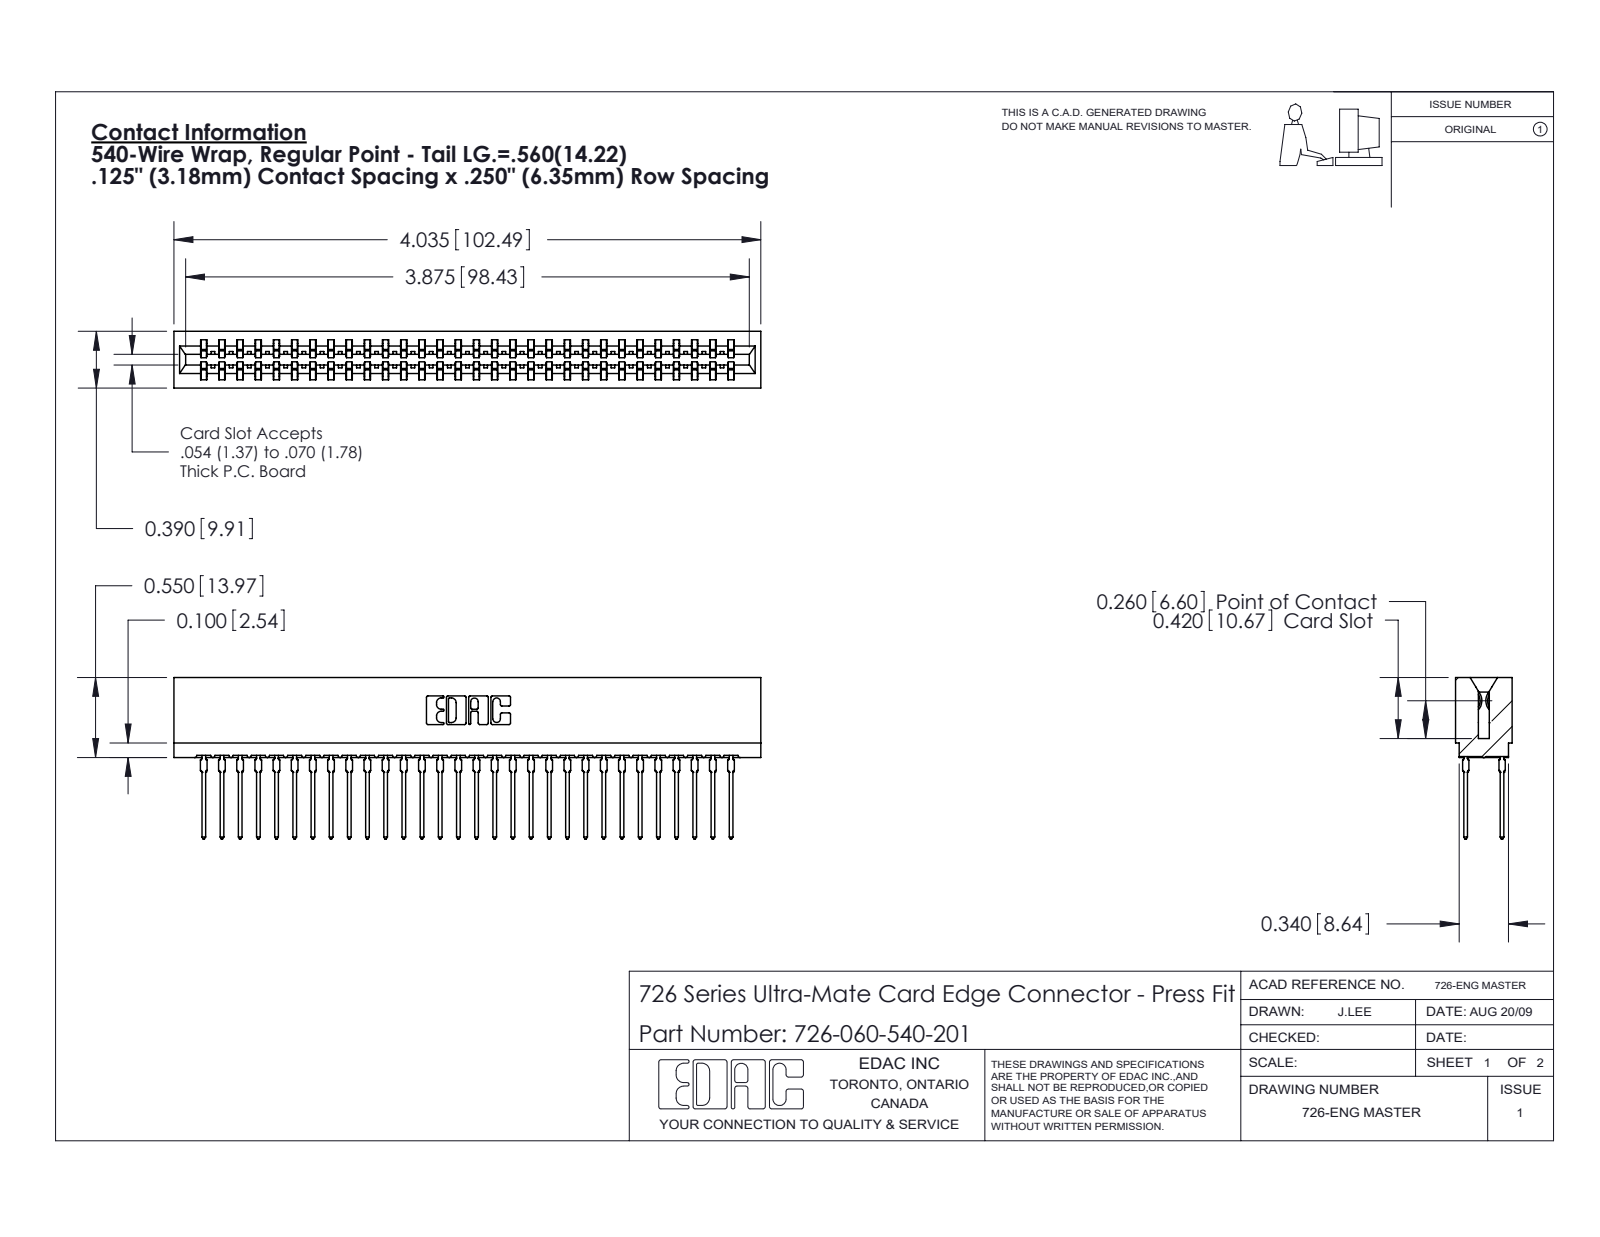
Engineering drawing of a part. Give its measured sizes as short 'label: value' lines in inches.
name: 726 Part_.515 Slot Depth - 01; 746-292-001_540; 726-060-540-201
written by: SolidWorks 2020 (CONFIG_CONTROL_DESIGN)
unit: in
bodies: 61 solids, 5467 faces (2815 planar, 1092 cylindrical, 1560 other)
size: 4.035 × 1.109 × 0.39
volume: 0.591 in³; area: 25.97 in²
rounds: 120× R0.021, 31× R0.015, 22× R0.01, 8× R0.005, 8× R0.011, 6× R0.007, 6× R0.031, 3× R0.026
face distances: 0.057, 0.333, 0.25, 0.025, 0.307, 0.39, 0.083, 0.275, 0.5, 0.75
